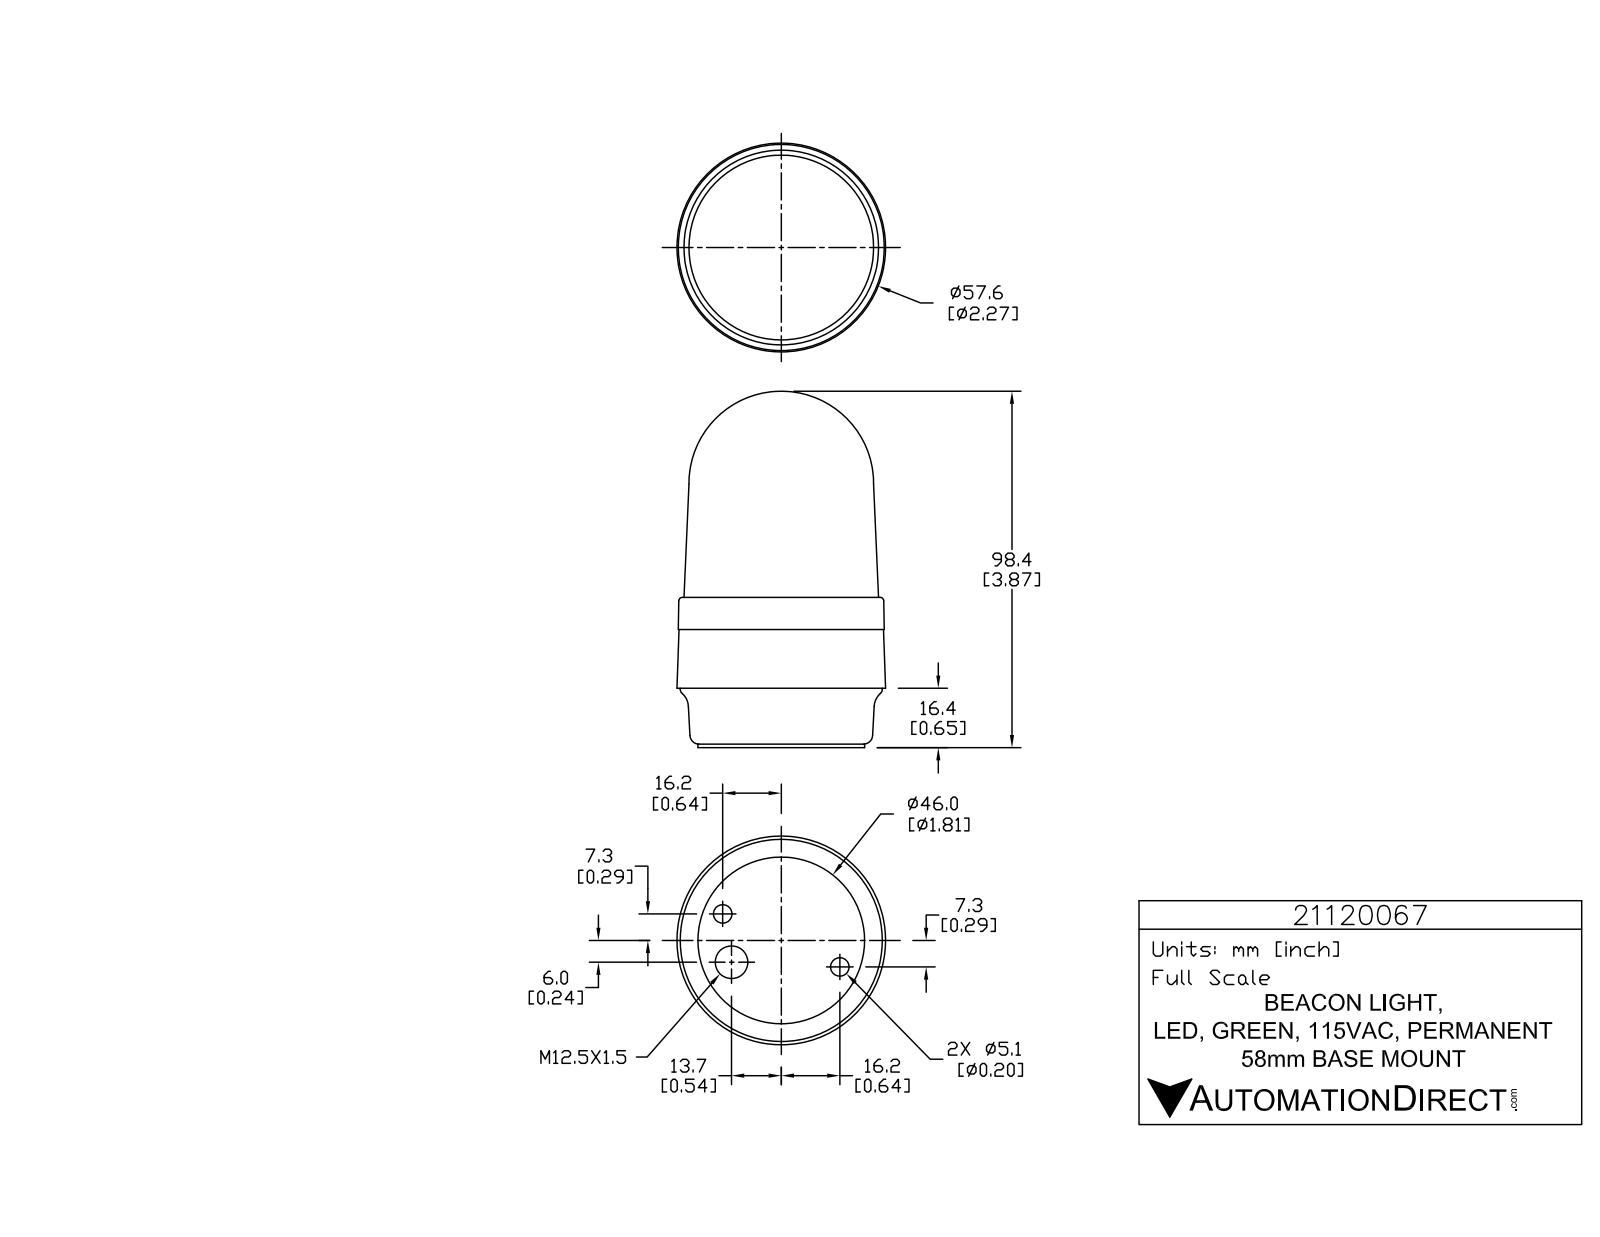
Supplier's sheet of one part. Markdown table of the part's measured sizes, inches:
| quantity | value |
| --- | --- |
| part name | 21120067 |
| STEP written by | SolidWorks 2015 (AUTOMOTIVE_DESIGN) |
| units | inches |
| bodies | 1 solid, 764 faces (527 planar, 145 cylindrical, 92 other) |
| overall size | 3.874 × 2.269 × 2.269 |
| volume | 12.2 in³ |
| surface area | 29.33 in² |
| round holes (diameter × count) | 0.039 × 3, 0.201 × 2, 0.354 × 1 |
| round bosses / shafts (diameter × count) | 0.226 × 3, 0.056 × 3, 2.197 × 1, 1.811 × 1 |
| partial cylindrical surfaces (radius × count) | 0.008 × 6, 0.008 × 6, 0.008 × 6, 0.131 × 6, 0.004 × 3, 0.005 × 3, 0.007 × 3, 0.008 × 3 |
| main face-to-face distances | 0.646, 0.039, 0.606, 1.634, 1.594, 0.988, 1.283, 1.244, 0.638, 0.35 |
| hole center spacings | 0.534, 1.179, 1.398 |
